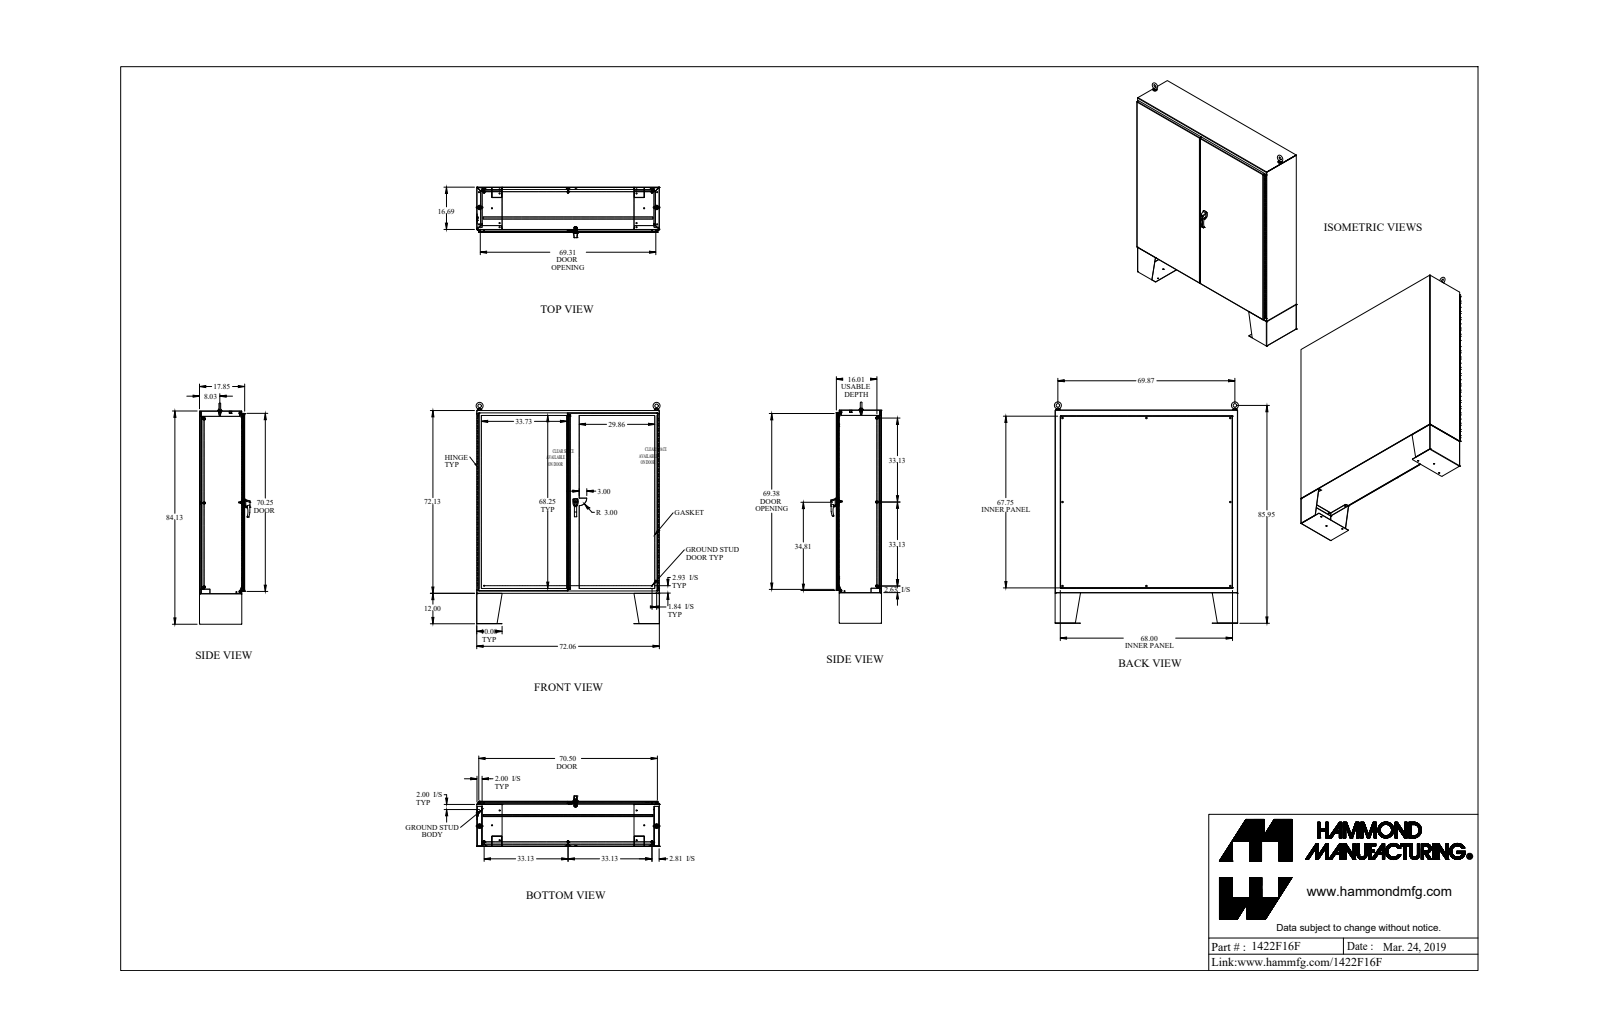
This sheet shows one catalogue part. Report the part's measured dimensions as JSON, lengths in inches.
{"part_name": "1422F16F_Default", "step_written_by": "SolidWorks 2019 (CONFIG_CONTROL_DESIGN)", "units": "inches", "bodies": {"solids": 92, "faces": 2997, "planar": 1372, "cylindrical": 1378, "other": 247}, "overall_size": [87.778, 73.121, 19.963], "volume_in3": 2577, "surface_area_in2": 48045, "round_holes": [[0.304, 24], [0.437, 14], [0.307, 9], [0.563, 8], [0.445, 6], [0.11, 2], [0.25, 2], [0.257, 2], [0.28, 2], [0.281, 2], [0.313, 2], [0.39, 2]], "round_bosses_or_shafts": [[1, 10], [0.65, 8], [0.375, 8], [0.33, 8], [0.281, 6], [0.25, 4], [1.75, 2], [1.5, 2]], "partial_cylinders_radius": [[0.048, 32], [0.143, 32], [0.125, 22], [0.018, 16], [0.06, 14], [0.116, 12], [0.05, 8], [0.185, 8]], "face_to_face_distances": [0.095, 0.125, 17.753, 17.628, 17.723, 17.848, 0.125, 1.687, 16.036, 15.941], "hole_center_spacings": [6, 12, 18, 70.647, 24, 71.407, 66.25, 72.657]}
